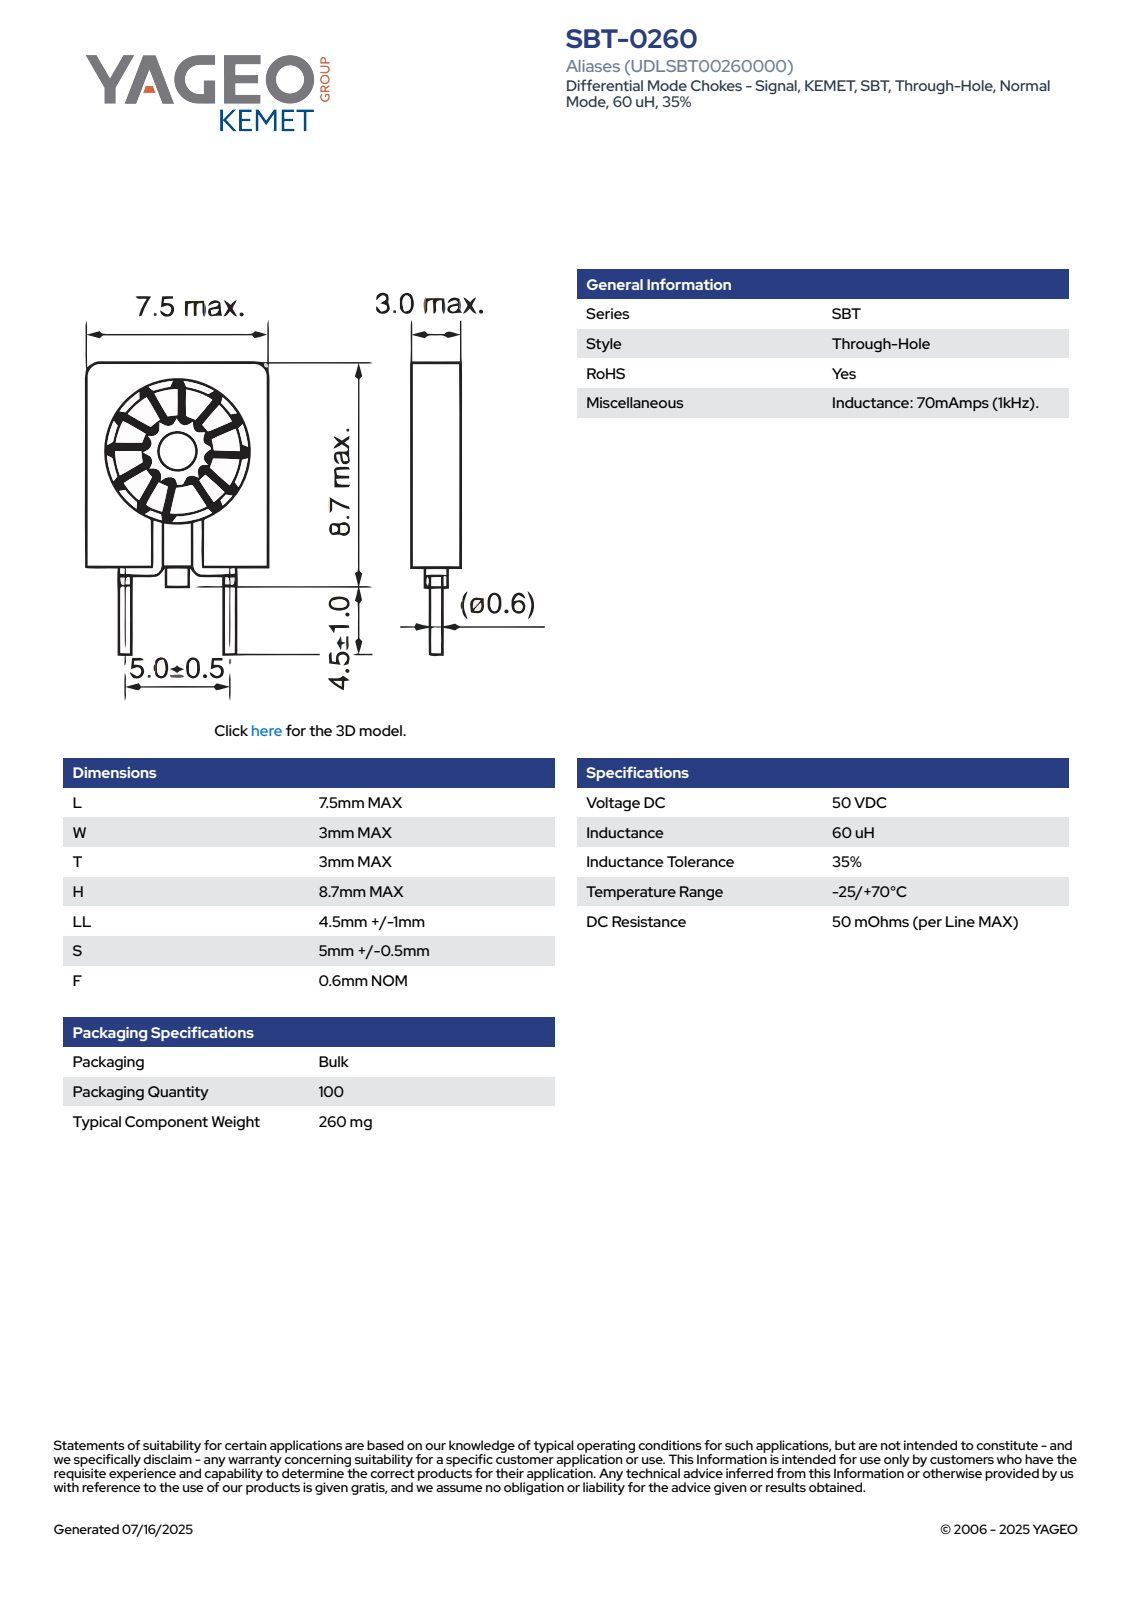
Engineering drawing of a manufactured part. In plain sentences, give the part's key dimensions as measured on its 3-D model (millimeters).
The part is named "IFC_NTSBT02_L7.5W3T3". Its 3-D file was written by "SolidWorks 2014 (AUTOMOTIVE_DESIGN)". It is 1 solid with 567 faces: 213 planar, 241 cylindrical and 113 other. Overall it measures 14.21 by 7.5 by 3 millimeters. Its volume is 151 cubic millimeters and its surface area 418 square millimeters. Round holes: 1 of diameter 2.37, 1 of diameter 6.39. Round bosses or shafts: 2 of diameter 0.6, 1 of diameter 5.58, 1 of diameter 1.76. Partial cylindrical surfaces (rounded edges, fillets, slot ends): 18 of radius 0.5, 16 of radius 0.52, 16 of radius 0.7, 16 of radius 0.72, 15 of radius 0.25. The main face-to-face distances are 7.5, 3, 0.5, 2.5, 8, 2.91, 2.26, 5.24, 2.8, 2.3.
